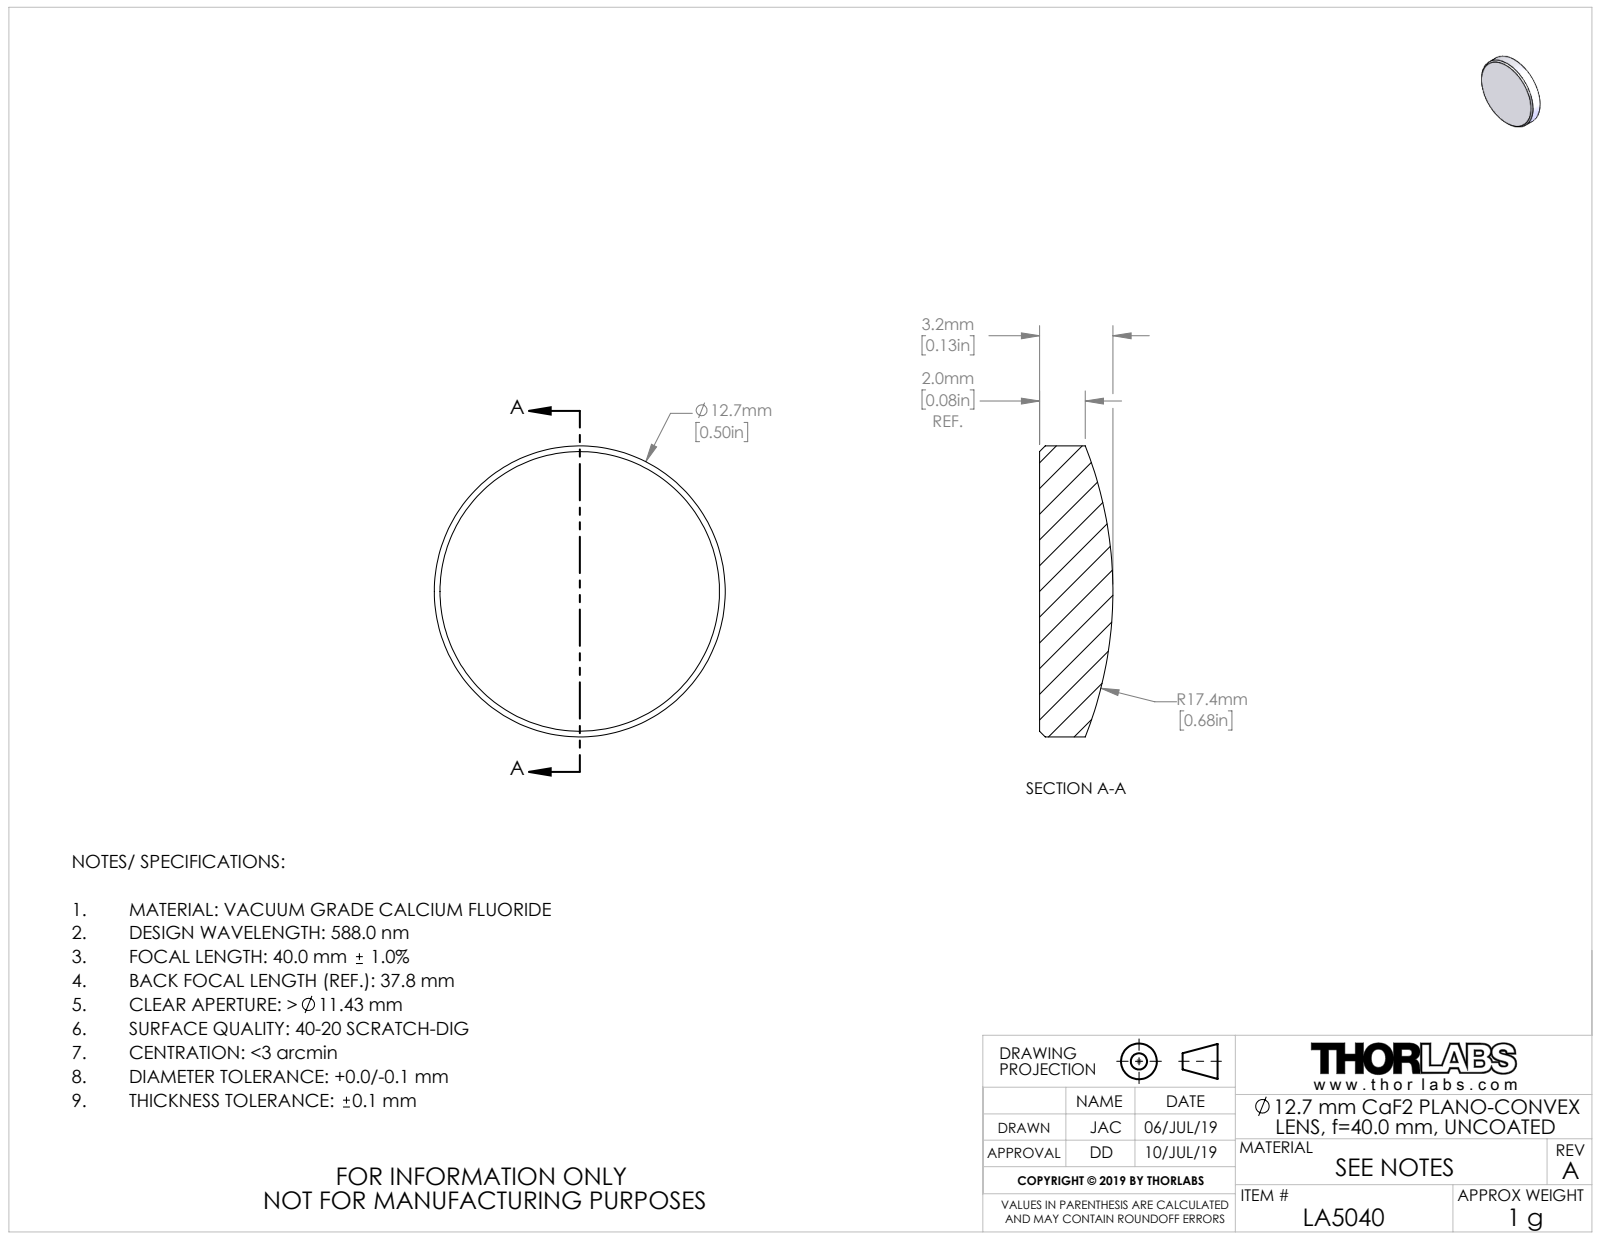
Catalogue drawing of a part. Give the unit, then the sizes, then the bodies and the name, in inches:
Units: inches
Overall size (bounding box): 0.5 × 0.5 × 0.126
Round bosses / shafts (diameter × count): ⌀0.5 ×1
Volume: 0.02 in³ · Surface area: 0.515 in²
Bodies: 1 solid, 7 faces (1 planar, 2 cylindrical, 4 other)
Part name (STEP PRODUCT): TTN188113-E0W
STEP written by: SolidWorks 2018 (CONFIG_CONTROL_DESIGN)
